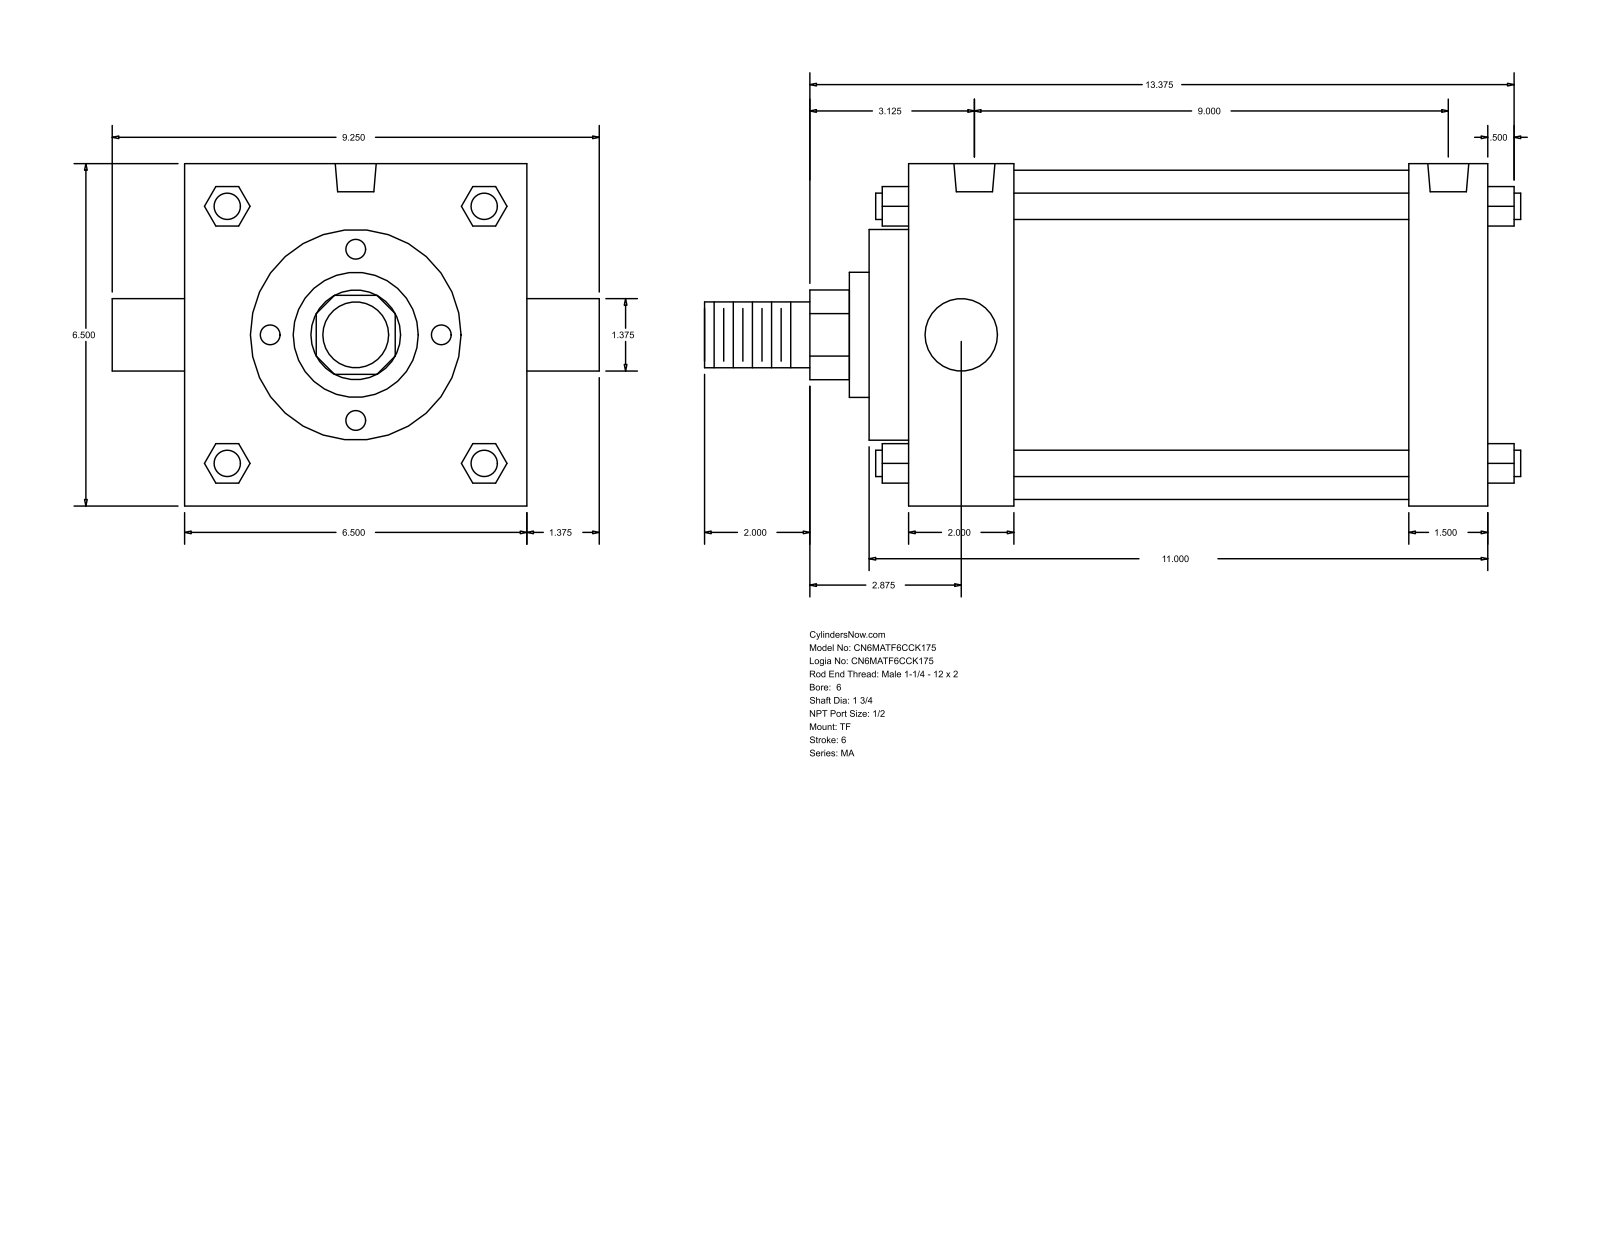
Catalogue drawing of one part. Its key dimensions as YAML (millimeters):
part_name: "MA_TF__0600_1.75"
step_written_by: "GSSL Pune (CONFIG_CONTROL_DESIGN)"
units: millimeters
bodies: {solids: 0, faces: 122, planar: 93, cylindrical: 29, other: 0}
overall_size: [393.7, 234.95, 165.1]
round_holes:
  - {diameter: 17.46, count: 3}
  - {diameter: 19.77, count: 2}
round_bosses_or_shafts:
  - {diameter: 12.7, count: 4}
  - {diameter: 158.75, count: 1}
  - {diameter: 101.6, count: 1}
  - {diameter: 60.33, count: 1}
  - {diameter: 44.45, count: 1}
  - {diameter: 34.92, count: 1}
  - {diameter: 31.75, count: 1}
partial_cylinders:
  - {radius: 21.63, count: 1}
face_to_face_distances: [165.1, 279.4, 19.05, 50.8, 241.31, 228.6, 190.51, 38.09, 69.85, 260.36]
hole_center_spacings: [228.6]
